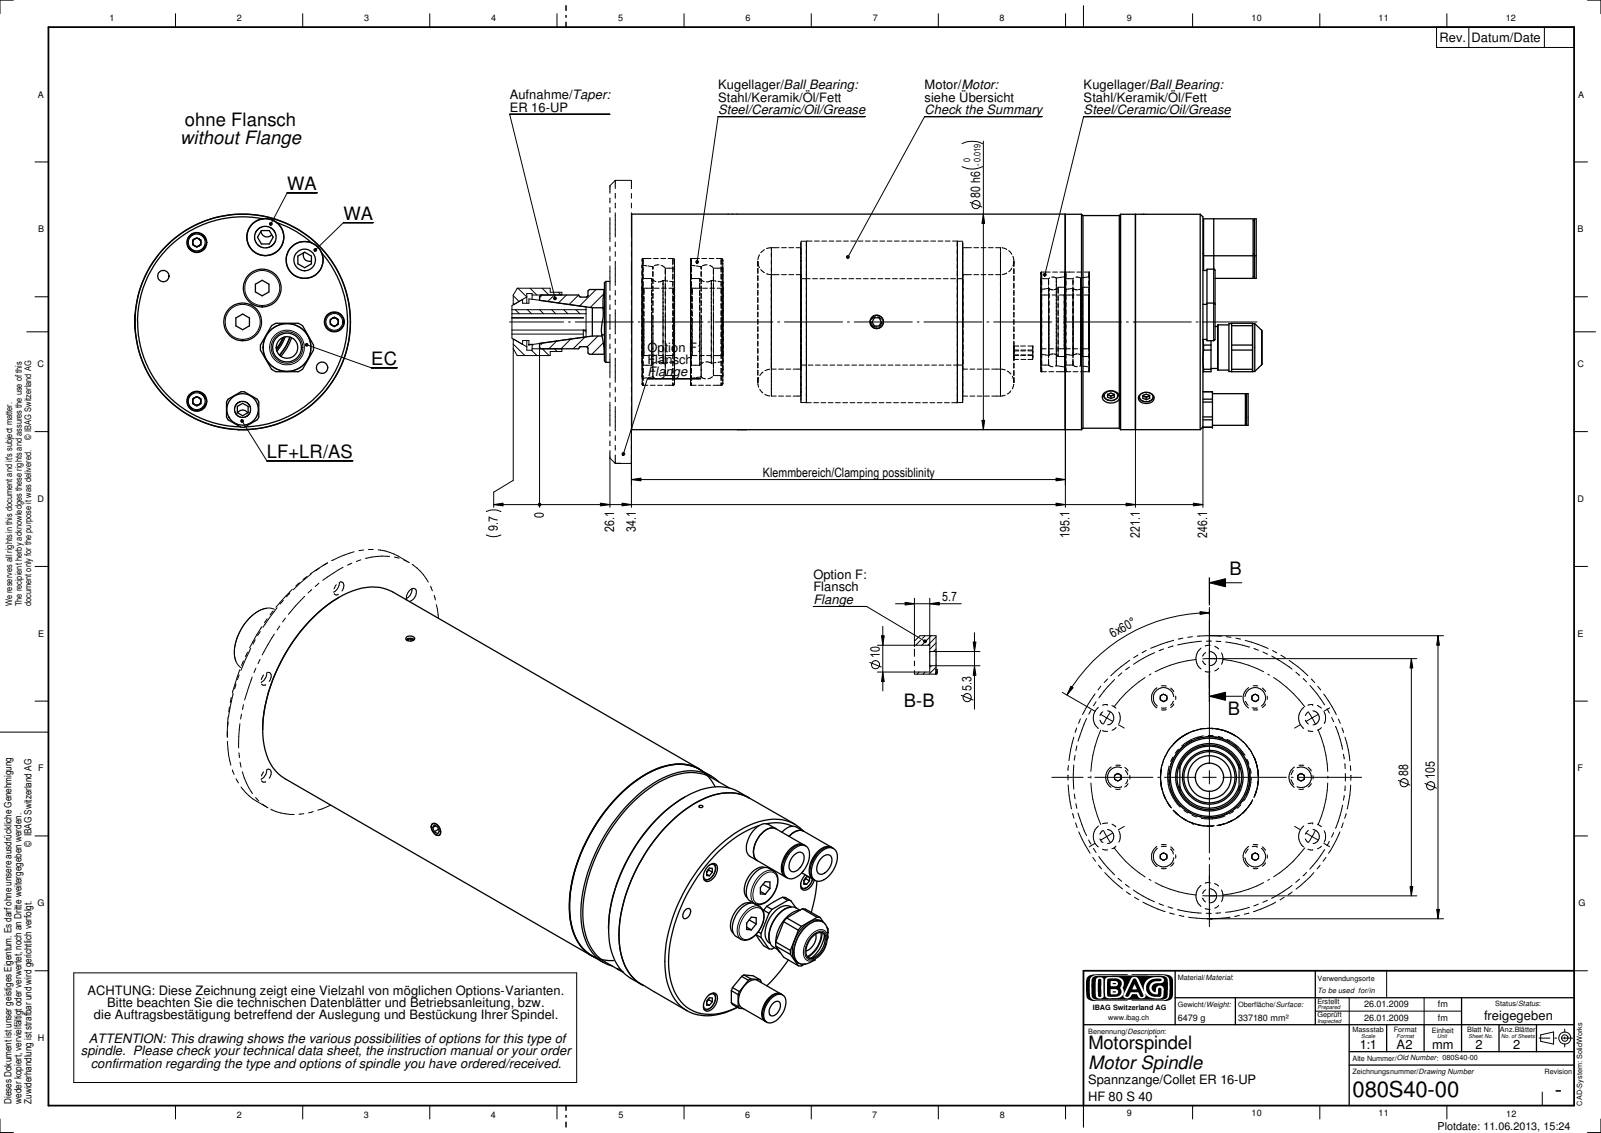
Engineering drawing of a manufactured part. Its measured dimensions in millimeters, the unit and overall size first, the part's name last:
Units: millimetres
Overall size (bounding box): 278.36 × 80 × 80
Round holes (diameter × count): ⌀7.4 ×3, ⌀8 ×3, ⌀4.2 ×2, ⌀6 ×2, ⌀1.5 ×1, ⌀3.3 ×1, ⌀5.9 ×1, ⌀6.5 ×1, ⌀10.7 ×1, ⌀16.2 ×1, ⌀30.2 ×1
Round bosses / shafts (diameter × count): ⌀7.64 ×6, ⌀14 ×2, ⌀13.7 ×2, ⌀13.7 ×2, ⌀13 ×2, ⌀80 ×1, ⌀79.9 ×1, ⌀79.8 ×1
Partial cylindrical surfaces — rounded edges, fillets, slot ends (radius × count): R6.6 ×1, R9.9 ×1, R12 ×1
Main face-to-face distances: 220, 8, 212, 195, 187, 25, 51, 169, 161, 26
Hole centre spacings: 34, 32.5, 40.5, 48.08, 52.76, 58.89, 65.68, 13.1
Bodies: 0 solids, 411 faces (184 planar, 128 cylindrical, 99 other)
Part name (STEP PRODUCT): 080S40-00
STEP written by: SolidWorks 2012 (CONFIG_CONTROL_DESIGN)
